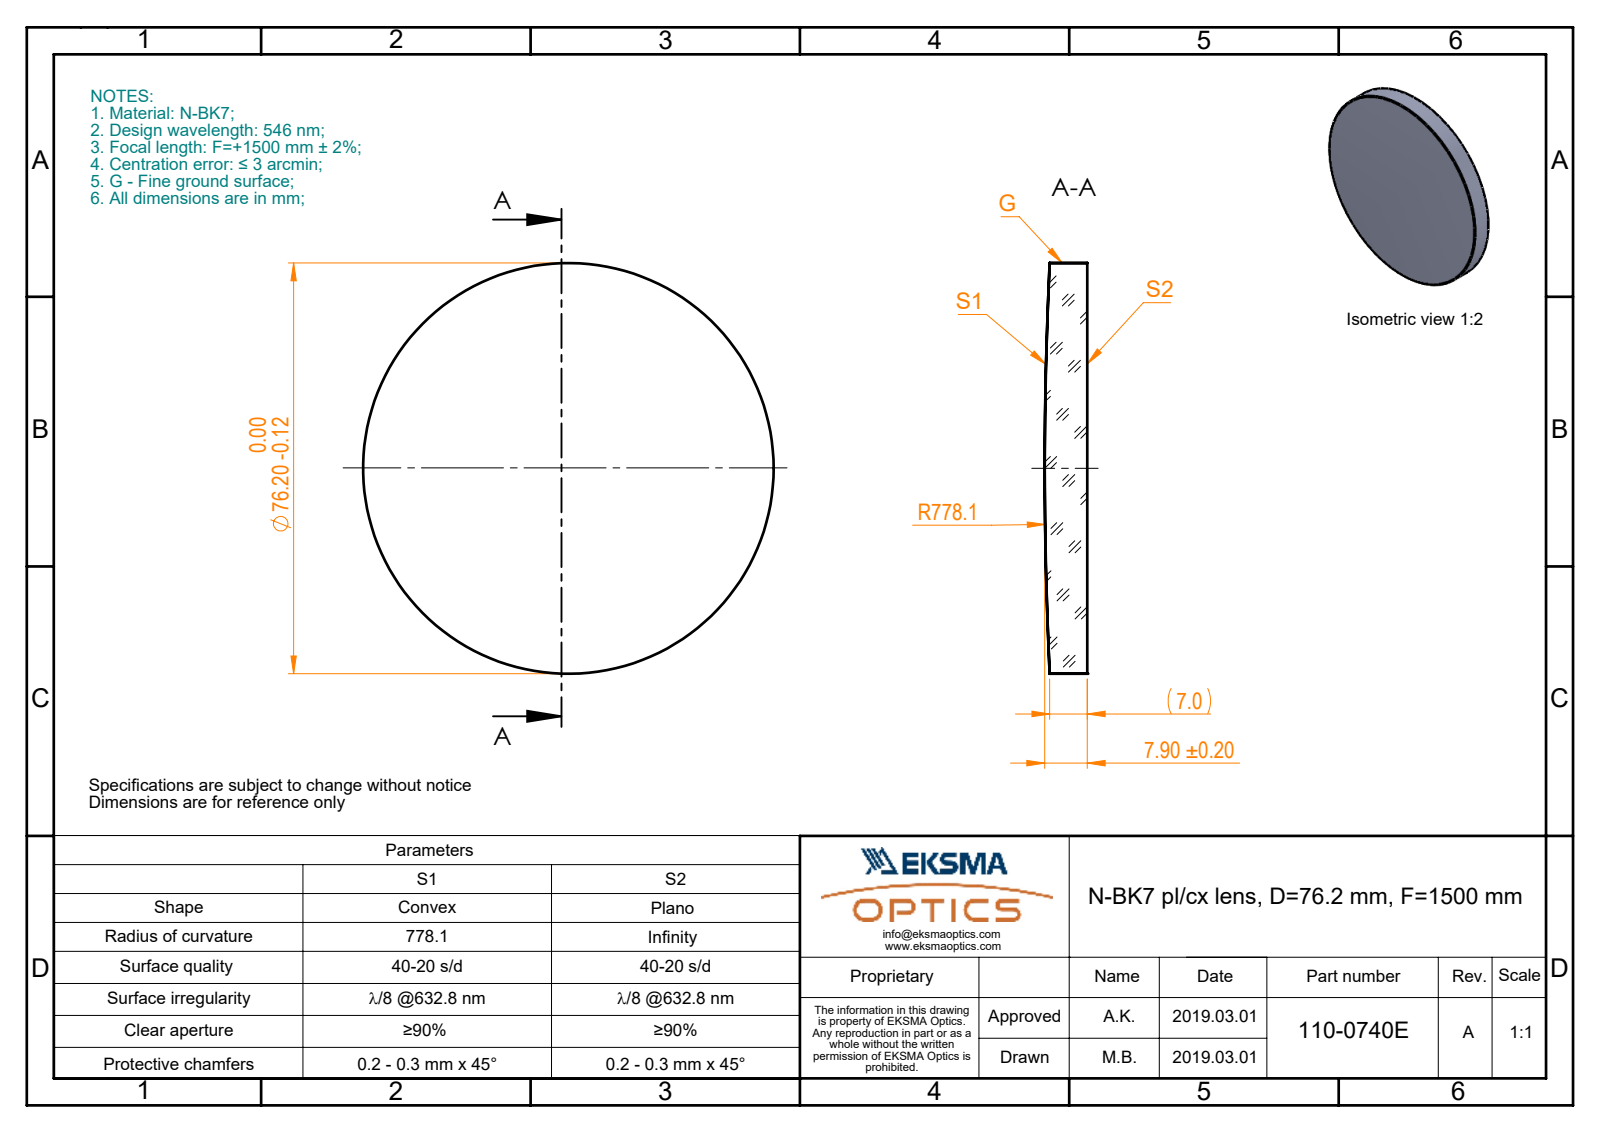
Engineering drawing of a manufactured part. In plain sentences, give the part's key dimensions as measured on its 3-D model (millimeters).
The part is named "110-0740E BK7 pl-cx 76.2 F1500". Its 3-D file was written by "SolidWorks 2017 (CONFIG_CONTROL_DESIGN)". It is 1 solid with 5 faces: 1 planar, 2 cylindrical and 2 other. Overall it measures 76.2 by 76.2 by 7.9 millimeters. Its volume is 33 899 cubic millimeters and its surface area 10 791 square millimeters. Round bosses or shafts: 1 of diameter 76.2.
